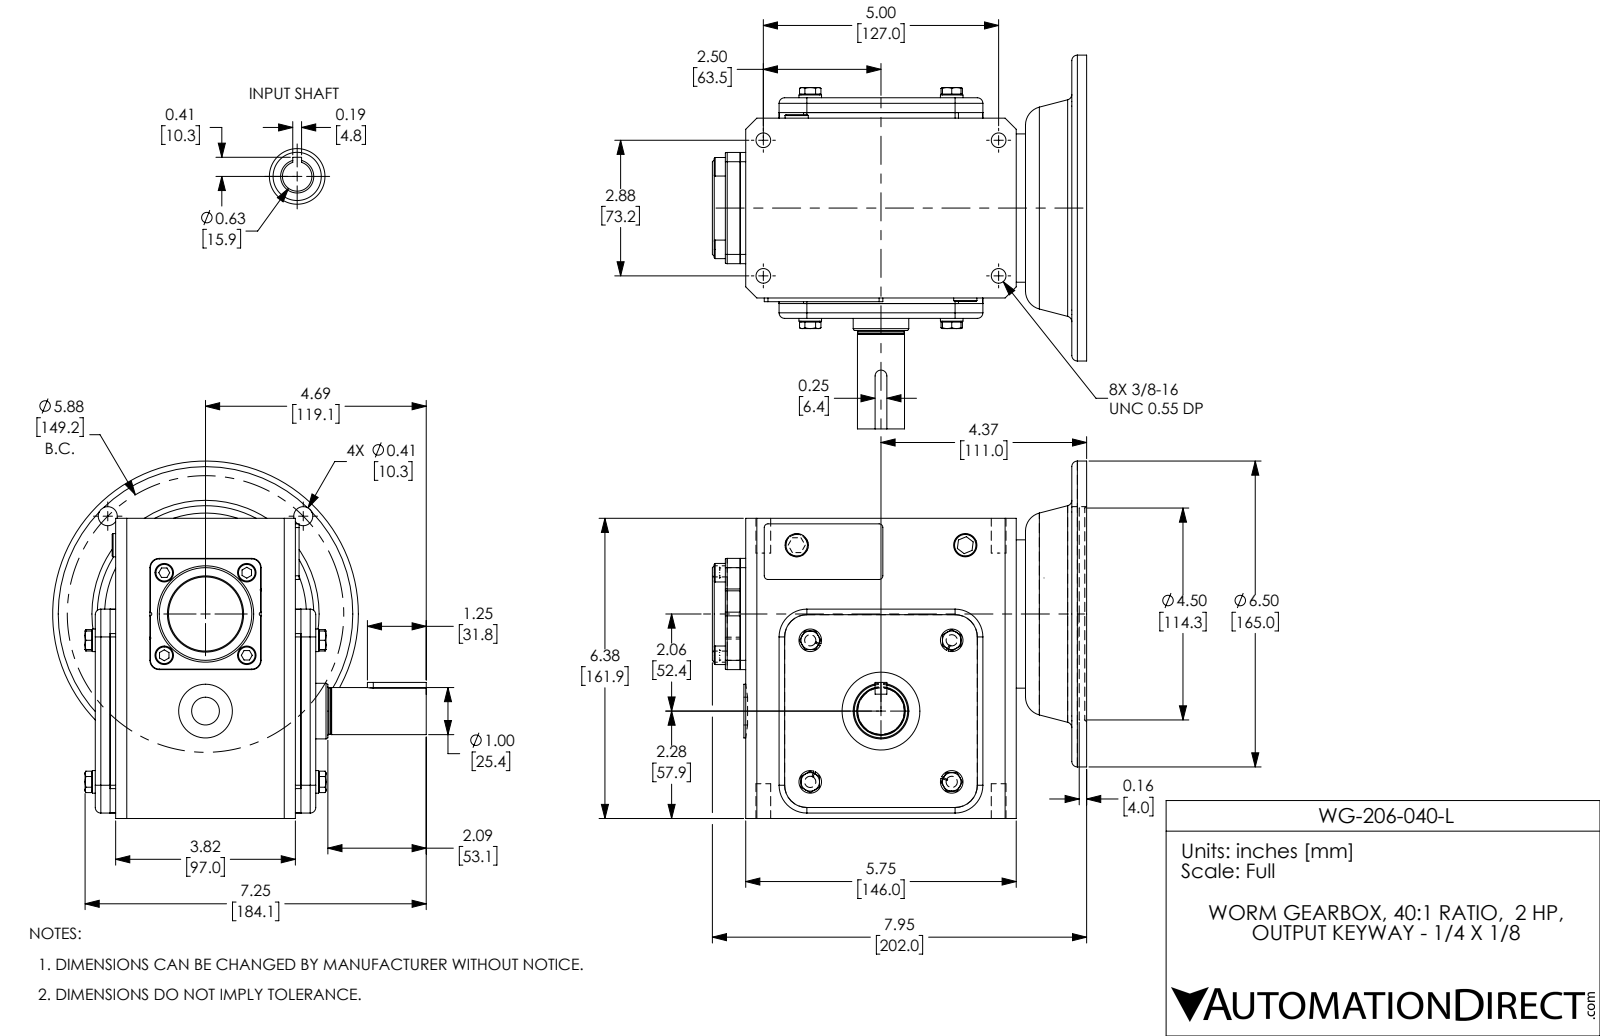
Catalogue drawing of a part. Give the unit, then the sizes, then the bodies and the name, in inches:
Units: inches
Overall size (bounding box): 7.953 × 7.938 × 7.591
Round holes (diameter × count): ⌀0.313 ×4, ⌀0.406 ×4, ⌀0.495 ×2, ⌀1.181 ×2, ⌀0.591 ×1, ⌀0.625 ×1, ⌀1.457 ×1, ⌀1.654 ×1, ⌀3.543 ×1, ⌀4.5 ×1
Round bosses / shafts (diameter × count): ⌀0.394 ×8, ⌀0.48 ×4, ⌀6.496 ×1, ⌀3.15 ×1, ⌀2.047 ×1, ⌀1.575 ×1, ⌀1.142 ×1, ⌀1 ×1
Partial cylindrical surfaces — rounded edges, fillets, slot ends (radius × count): R0.079 ×8, R0.118 ×8, R0.197 ×4, R0.591 ×4, R0.02 ×2, R0.039 ×2, R0.125 ×1, R2.717 ×1
Main face-to-face distances: 0.315, 0.118, 4.055, 4.37, 0.433, 3.937, 4.252, 6.375, 4.685, 0.709
Hole centre spacings: 2.937, 4.154, 2.077, 2.681, 2.88, 4.631, 5, 5.77
Volume: 169.4 in³ · Surface area: 418.2 in²
Bodies: 44 solids, 619 faces (303 planar, 188 cylindrical, 128 other)
Part name (STEP PRODUCT): WG-206-040-L
STEP written by: SolidWorks 2017 (AUTOMOTIVE_DESIGN)
